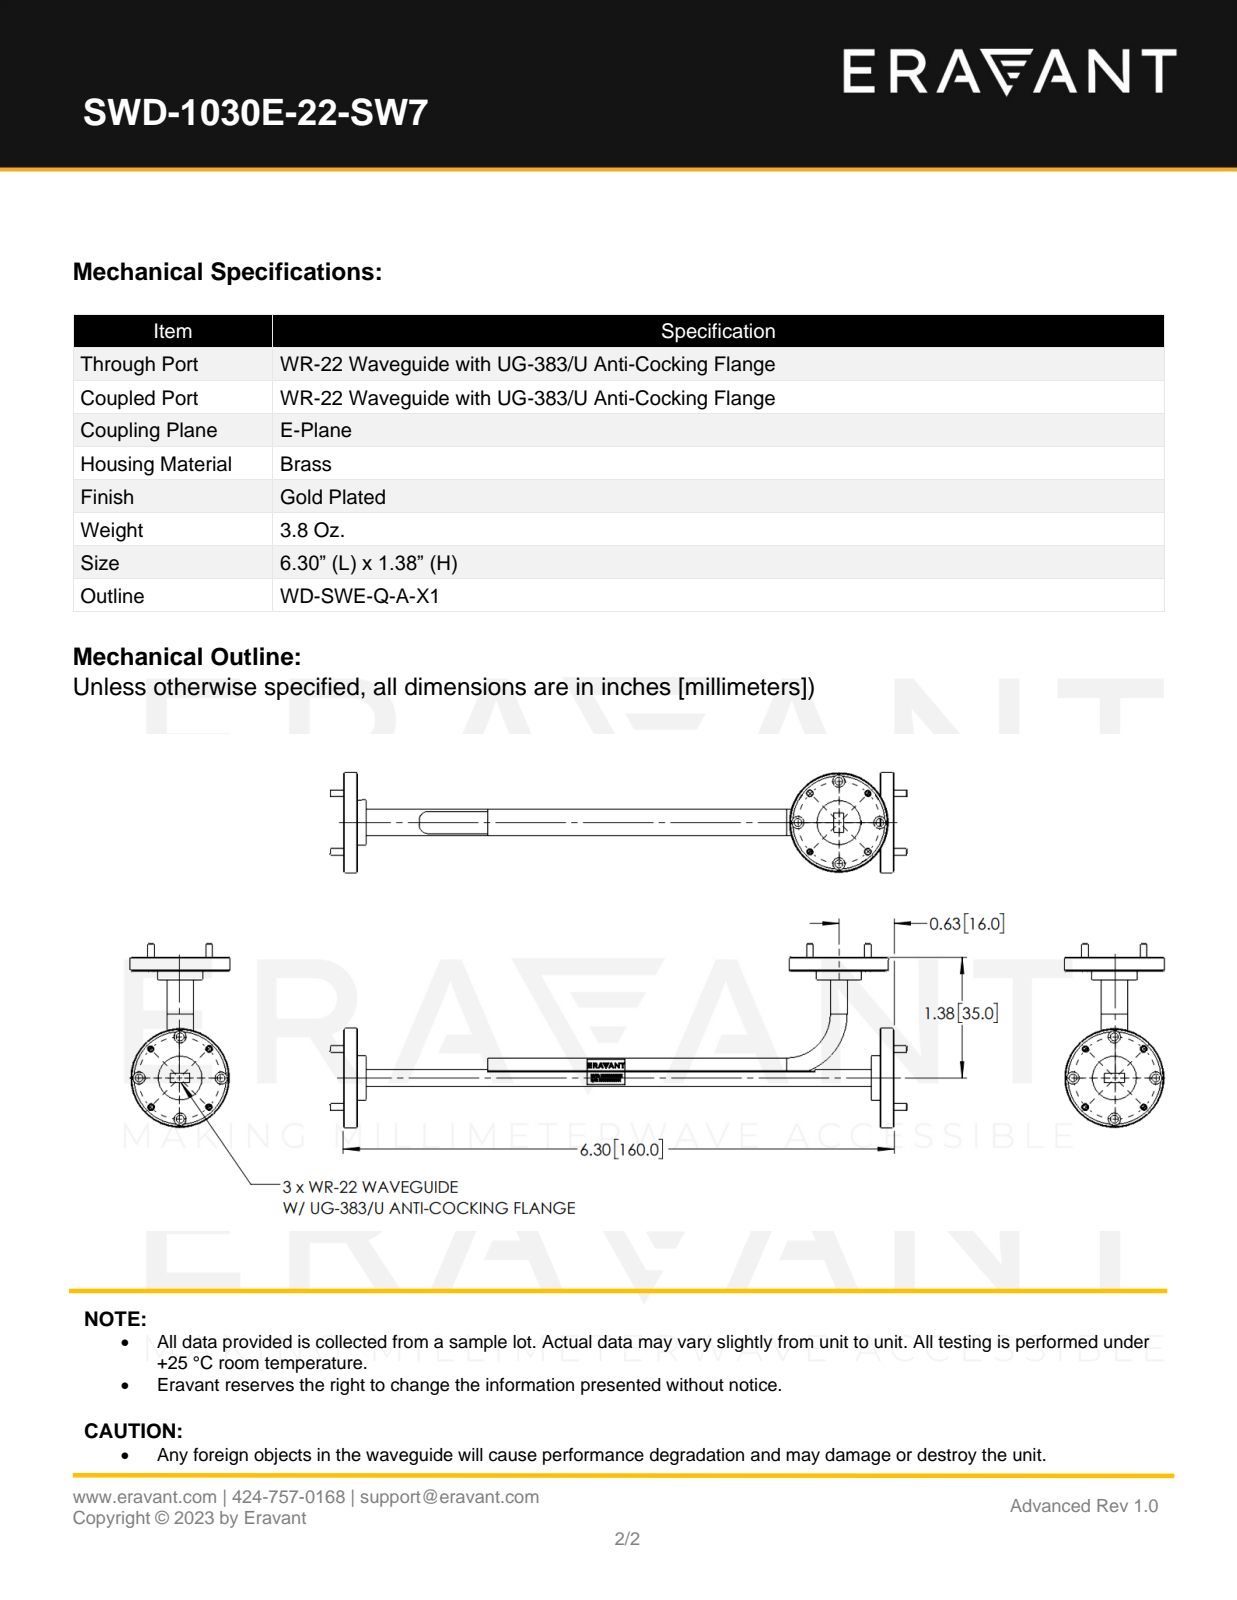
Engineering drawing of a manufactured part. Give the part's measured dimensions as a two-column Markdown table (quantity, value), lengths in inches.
| quantity | value |
| --- | --- |
| part name | WD-SWE-Q-A-X1 |
| STEP written by | SolidWorks 2021 (CONFIG_CONTROL_DESIGN) |
| units | inches |
| bodies | 7 solids, 245 faces (77 planar, 116 cylindrical, 52 other) |
| overall size | 6.604 × 2.093 × 1.125 |
| volume | 1.322 in³ |
| surface area | 18.75 in² |
| round holes (diameter × count) | 0.089 × 8, 0.14 × 8, 0.061 × 6, 0.067 × 6, 1.055 × 2 |
| round bosses / shafts (diameter × count) | 0.063 × 6, 1.125 × 2, 0.5 × 2 |
| partial cylindrical surfaces (radius × count) | 0.5 × 1, 0.692 × 1 |
| main face-to-face distances | 0.412, 0.14, 0.054, 0.358, 0.413, 5.979, 1.403, 0.99, 0.192, 6.279 |
| hole center spacings | 0.359, 0.866, 0.663, 0.469, 0.469, 0.937, 0.938, 0.663 |
